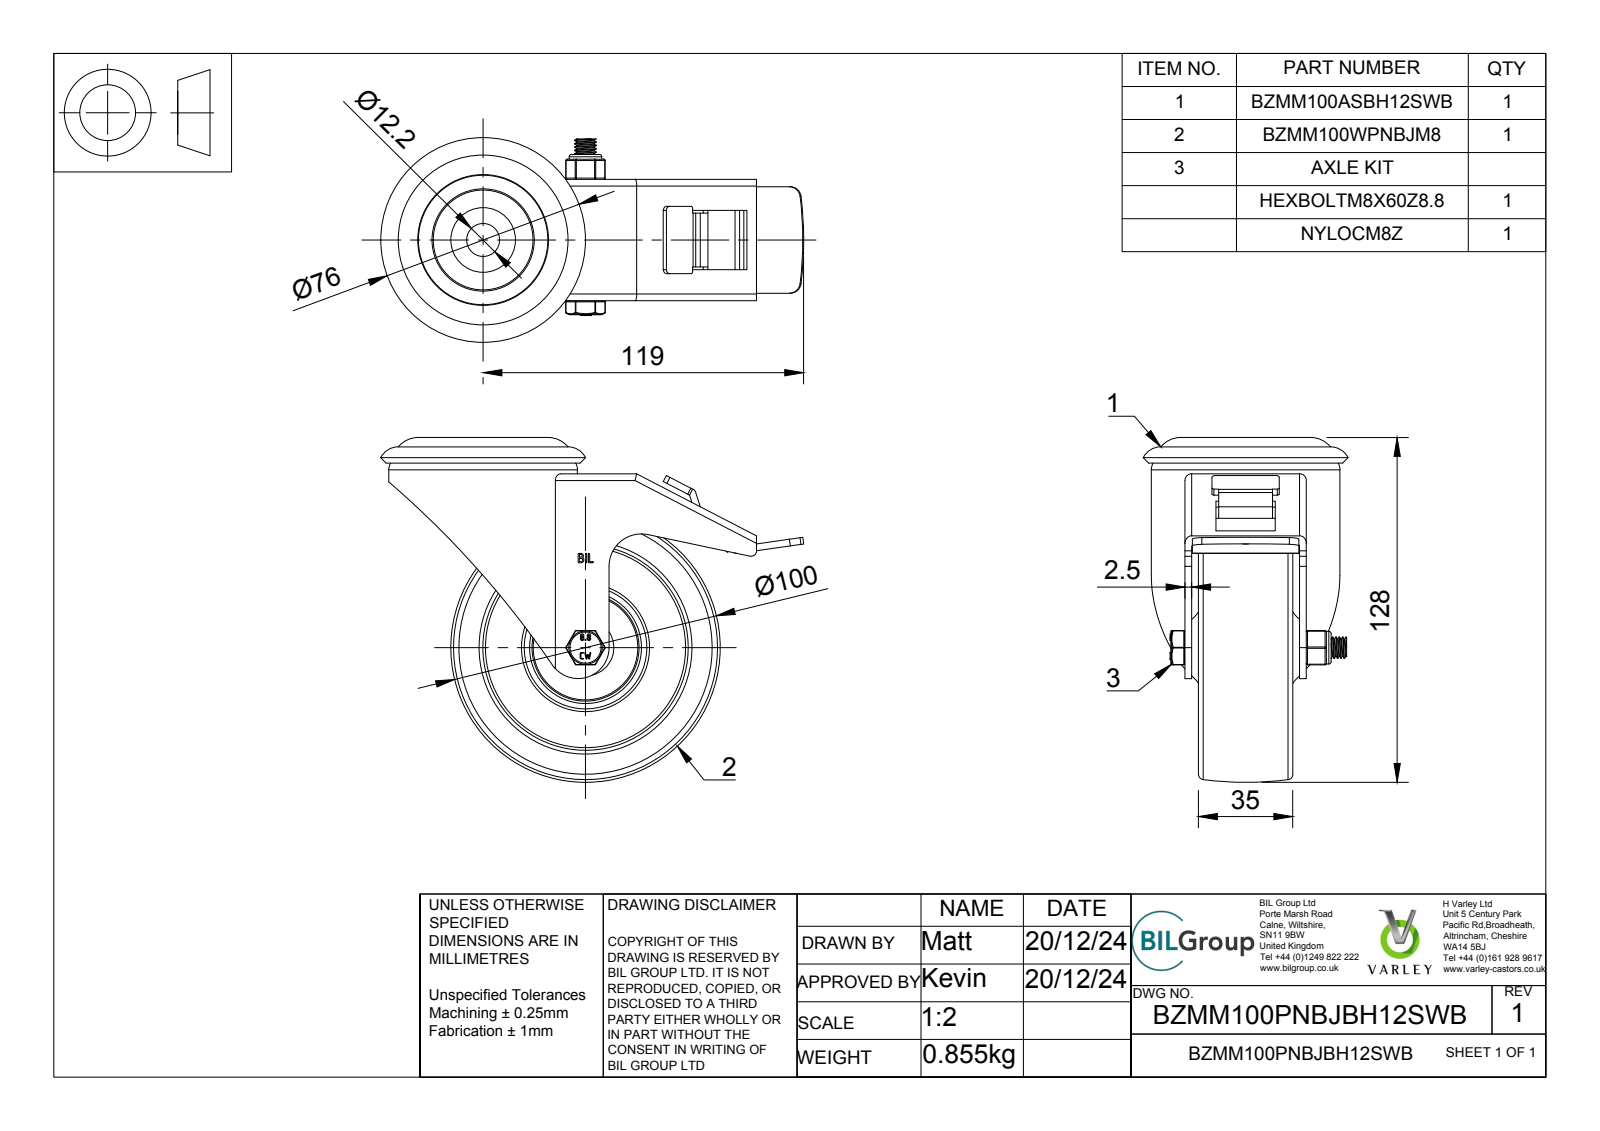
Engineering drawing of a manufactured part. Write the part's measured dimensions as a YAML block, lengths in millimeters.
part_name: "BZMM100PNBJBH12SWB v3; BZMM100ASBH12SWB v1; PRESSED STEEL, ZINC PLATED HEAD; PRESSED STEEL, ZINC PLATED FORKS (+8 more)"
step_written_by: "Autodesk Translation Framework v13.20.0.188 (AP242_MANAGED_MODEL_BASED_3D_ENGINEERING_MIM_LF)"
units: millimeters
bodies: {solids: 24, faces: 1009, planar: 466, cylindrical: 258, other: 285}
overall_size: [157, 128, 76]
volume: 234856
surface_area: 146655
round_holes:
  - {diameter: 0.66, count: 2}
  - {diameter: 8, count: 1}
  - {diameter: 8.2, count: 1}
  - {diameter: 8.4, count: 1}
  - {diameter: 8.6, count: 1}
  - {diameter: 12.2, count: 1}
  - {diameter: 15, count: 1}
  - {diameter: 20, count: 1}
  - {diameter: 22.5, count: 1}
  - {diameter: 26, count: 1}
  - {diameter: 30, count: 1}
  - {diameter: 31, count: 1}
round_bosses_or_shafts:
  - {diameter: 70, count: 1}
  - {diameter: 49.5, count: 1}
  - {diameter: 45.5, count: 1}
  - {diameter: 39.75, count: 1}
  - {diameter: 38, count: 1}
  - {diameter: 37, count: 1}
  - {diameter: 30.5, count: 1}
  - {diameter: 24, count: 1}
partial_cylinders:
  - {radius: 0.75, count: 50}
  - {radius: 0.5, count: 18}
  - {radius: 0.25, count: 12}
  - {radius: 1.25, count: 10}
  - {radius: 0.33, count: 4}
  - {radius: 0.64, count: 4}
  - {radius: 2.5, count: 4}
  - {radius: 2, count: 3}
face_to_face_distances: [2.5, 20, 5, 12, 40, 8, 17, 5.5, 25, 3]
hole_center_spacings: [4.65, 2.49]
